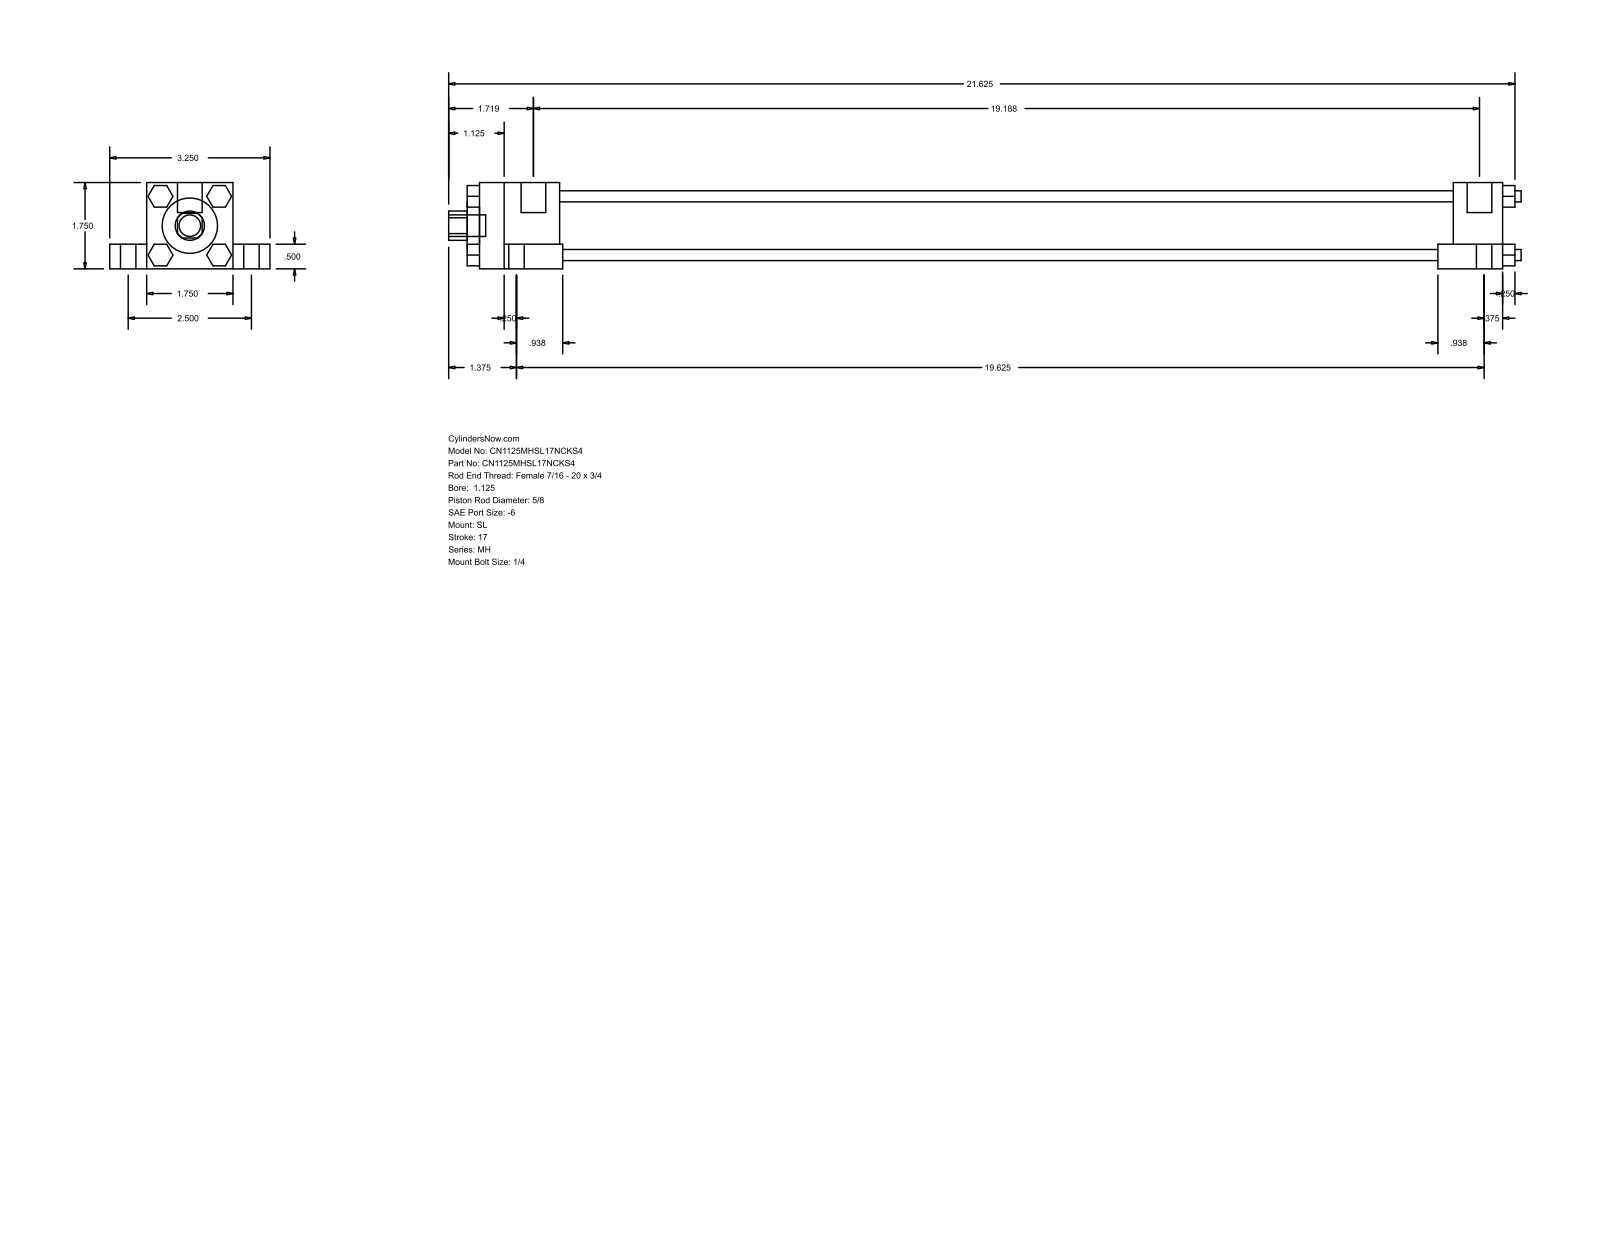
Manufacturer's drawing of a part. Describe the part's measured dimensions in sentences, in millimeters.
The part is named "MH_SL__0112_0.625". Its 3-D file was written by "GSSL Pune (CONFIG_CONTROL_DESIGN)". It is 0 solids with 150 faces: 114 planar, 36 cylindrical and 0 other. Overall it measures 552.45 by 82.55 by 44.45 millimeters. Round holes: 1 of diameter 15.88, 1 of diameter 28.57, 1 of diameter 34.92. Round bosses or shafts: 4 of diameter 14.29, 4 of diameter 7.94, 4 of diameter 5.71, 4 of diameter 5.56, 2 of diameter 12.7, 1 of diameter 11.11. Partial cylindrical surfaces (rounded edges, fillets, slot ends): 1 of radius 7.54. The main face-to-face distances are 44.46, 19.04, 12.7, 31.76, 63.5, 6.35, 533.39, 11.11, 460.37, 485.77.
